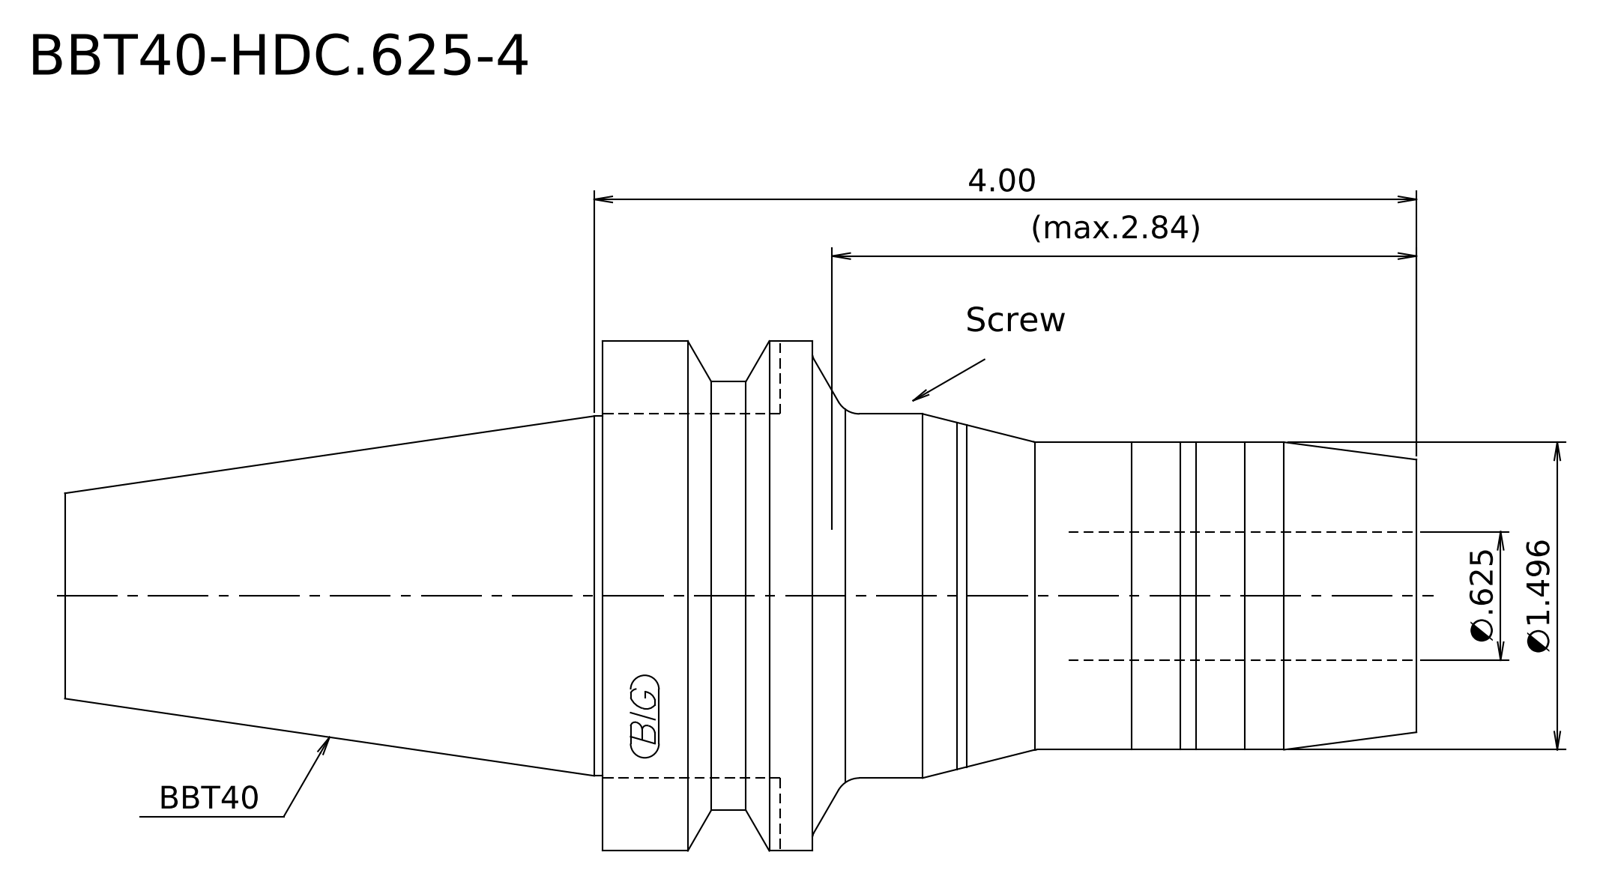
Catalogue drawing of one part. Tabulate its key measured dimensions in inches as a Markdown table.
| quantity | value |
| --- | --- |
| STEP written by | Kubotek KeyCreator 2011 V10.0.2 (22737) (automotive_design) |
| units | inches |
| bodies | 1 solid, 16 faces (4 planar, 6 cylindrical, 6 other) |
| overall size | 6.575 × 2.48 × 2.48 |
| volume | 14.36 in³ |
| surface area | 41.36 in² |
| round bosses / shafts (diameter × count) | 2.48 × 1, 2.087 × 1, 1.772 × 1, 1.75 × 1, 1.496 × 1 |
| main face-to-face distances | 3.961, 6.575, 2.614, 2.937, 1.024, 3.638 |
